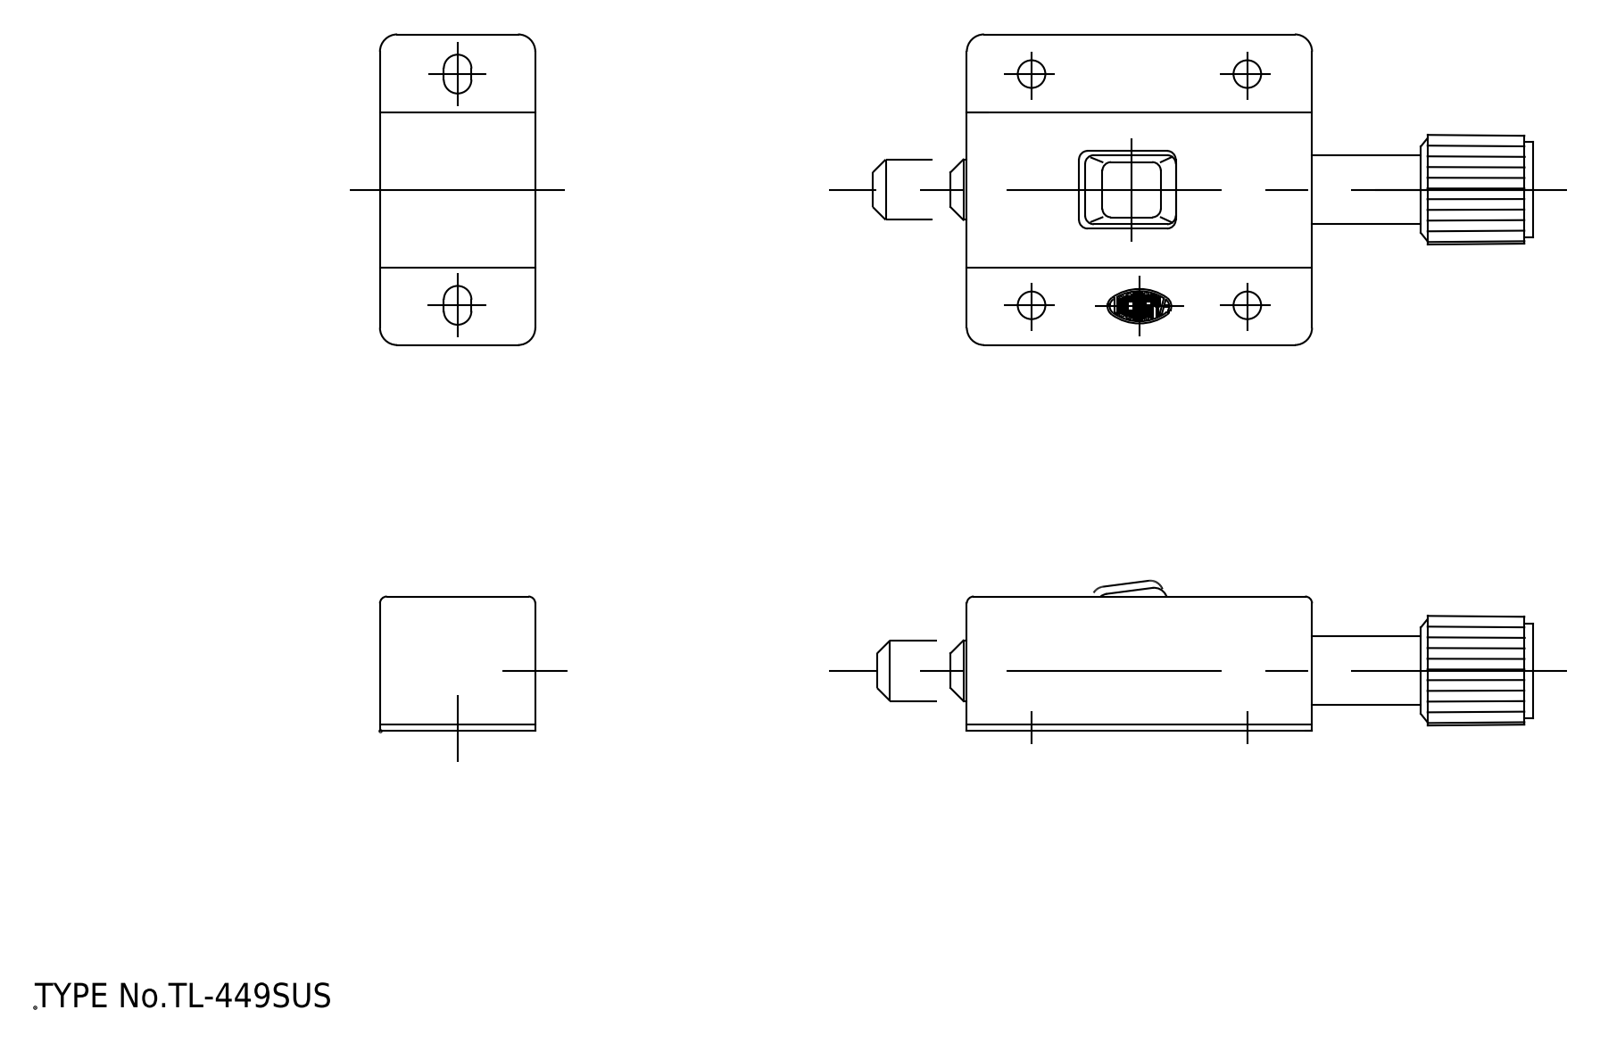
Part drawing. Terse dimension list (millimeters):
name: ケース; ロックボルト; TL_449SUS_K
written by: spGate 19.8.4 (****-****-****-****) (AUTOMOTIVE_DESIGN)
unit: mm
bodies: 3 solids, 130 faces (54 planar, 66 cylindrical, 10 other)
size: 95.43 × 36 × 16.61
volume: 7 734 mm³; area: 11 633 mm²
holes: 4× ⌀3.2, 1× ⌀8
bosses: 1× ⌀11, 1× ⌀7
rounds: 10× R2, 4× R0.5, 4× R0.8, 4× R1.6, 2× R0.95, 2× R1.2, 2× R1.5, 2× R1.75
face distances: 0.8, 17.2, 14.8, 18, 16.4, 14, 15.6, 69.03, 29.83, 39.2
hole spacings: 25, 26.8, 36.65
